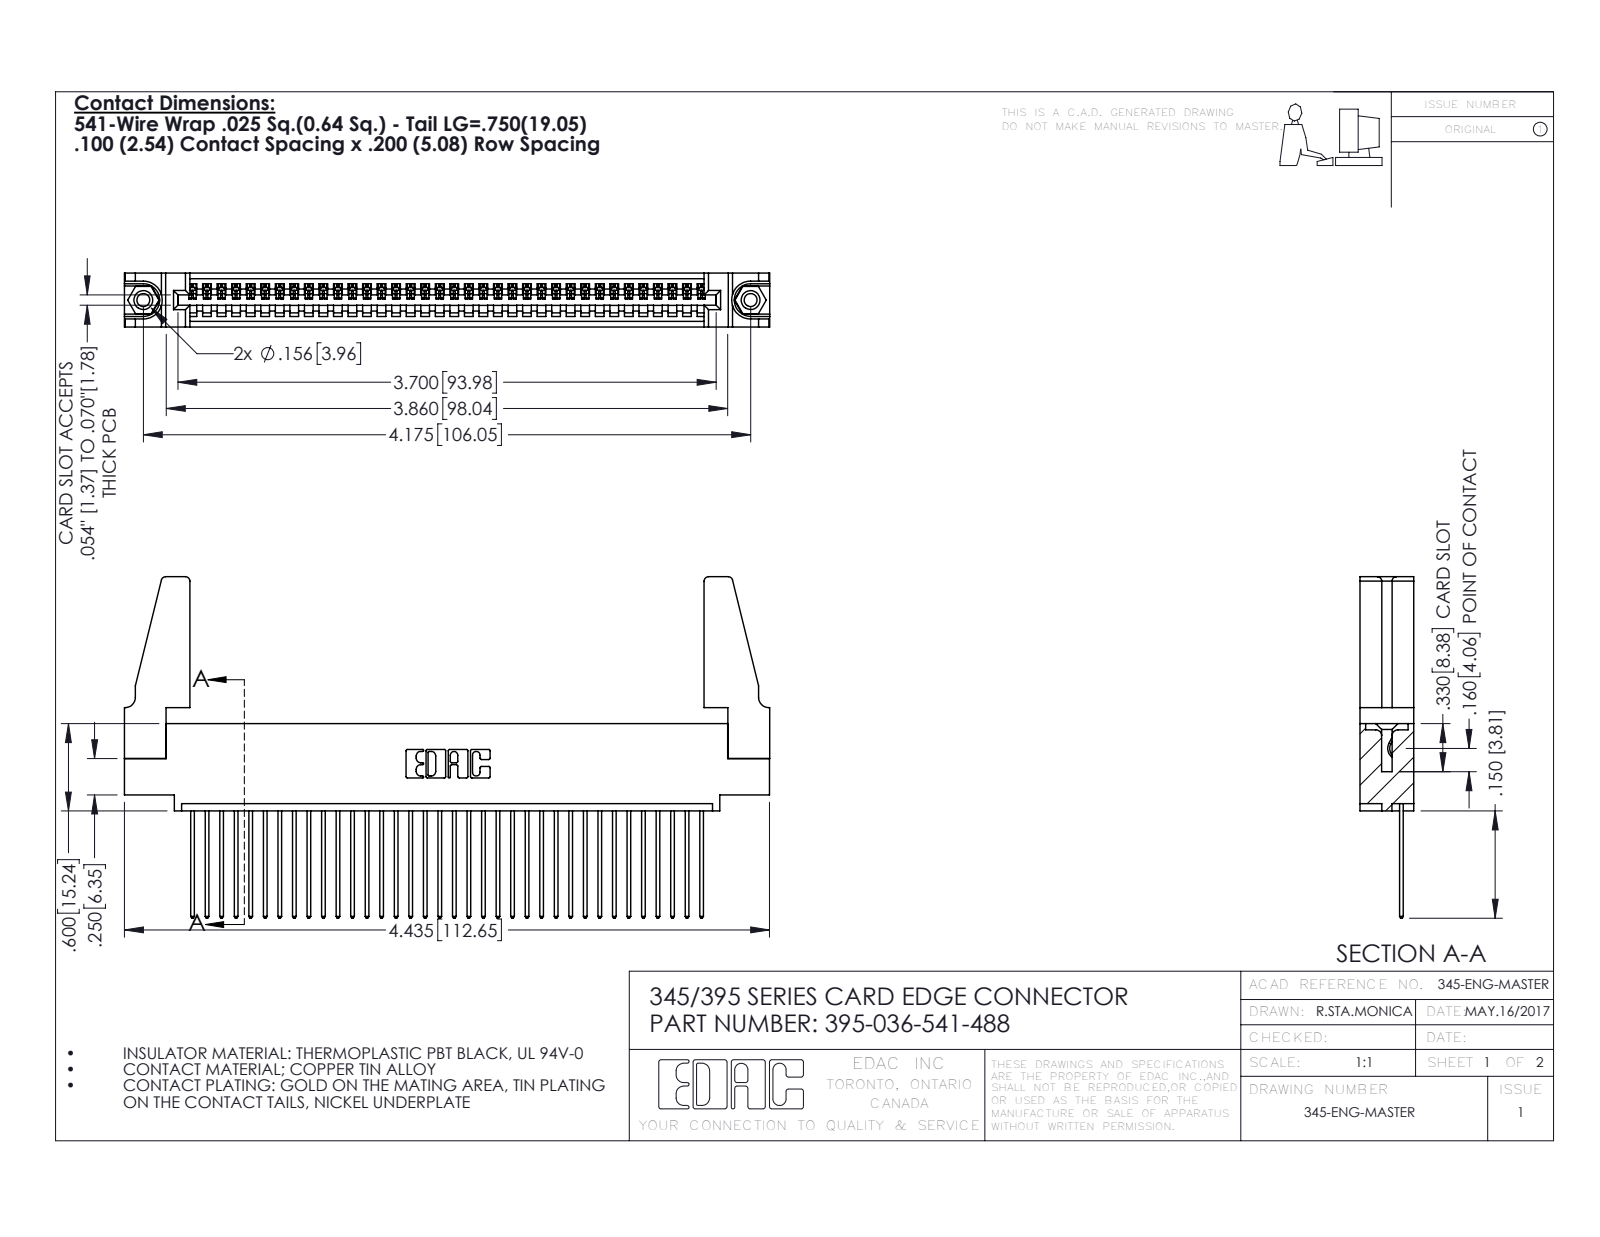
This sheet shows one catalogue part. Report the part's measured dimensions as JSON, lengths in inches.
{"part_name": "345-250-001_345-250-001-102; 345-220-078_345-220-088; 395-036-541-488; 345-292-001_345-293-141 (+1 more)", "step_written_by": "SolidWorks 2016 (CONFIG_CONTROL_DESIGN)", "units": "inches", "bodies": {"solids": 41, "faces": 2342, "planar": 1596, "cylindrical": 730, "other": 16}, "overall_size": [4.436, 2.347, 0.37], "volume_in3": 0.851, "surface_area_in2": 27.97, "round_holes": [[0.089, 2], [0.125, 2], [0.156, 2], [0.064, 1]], "round_bosses_or_shafts": [[0.155, 2]], "partial_cylinders_radius": [[0.006, 72], [0.01, 72], [0.01, 22], [0.03, 8], [0.007, 6], [0.031, 6], [0.026, 3], [0.031, 2]], "face_to_face_distances": [0.072, 0.298, 0.37, 0.098, 0.272, 0.025, 0.2, 0.225, 0.149, 0.072], "hole_center_spacings": [0.27, 3.939, 4.175]}
